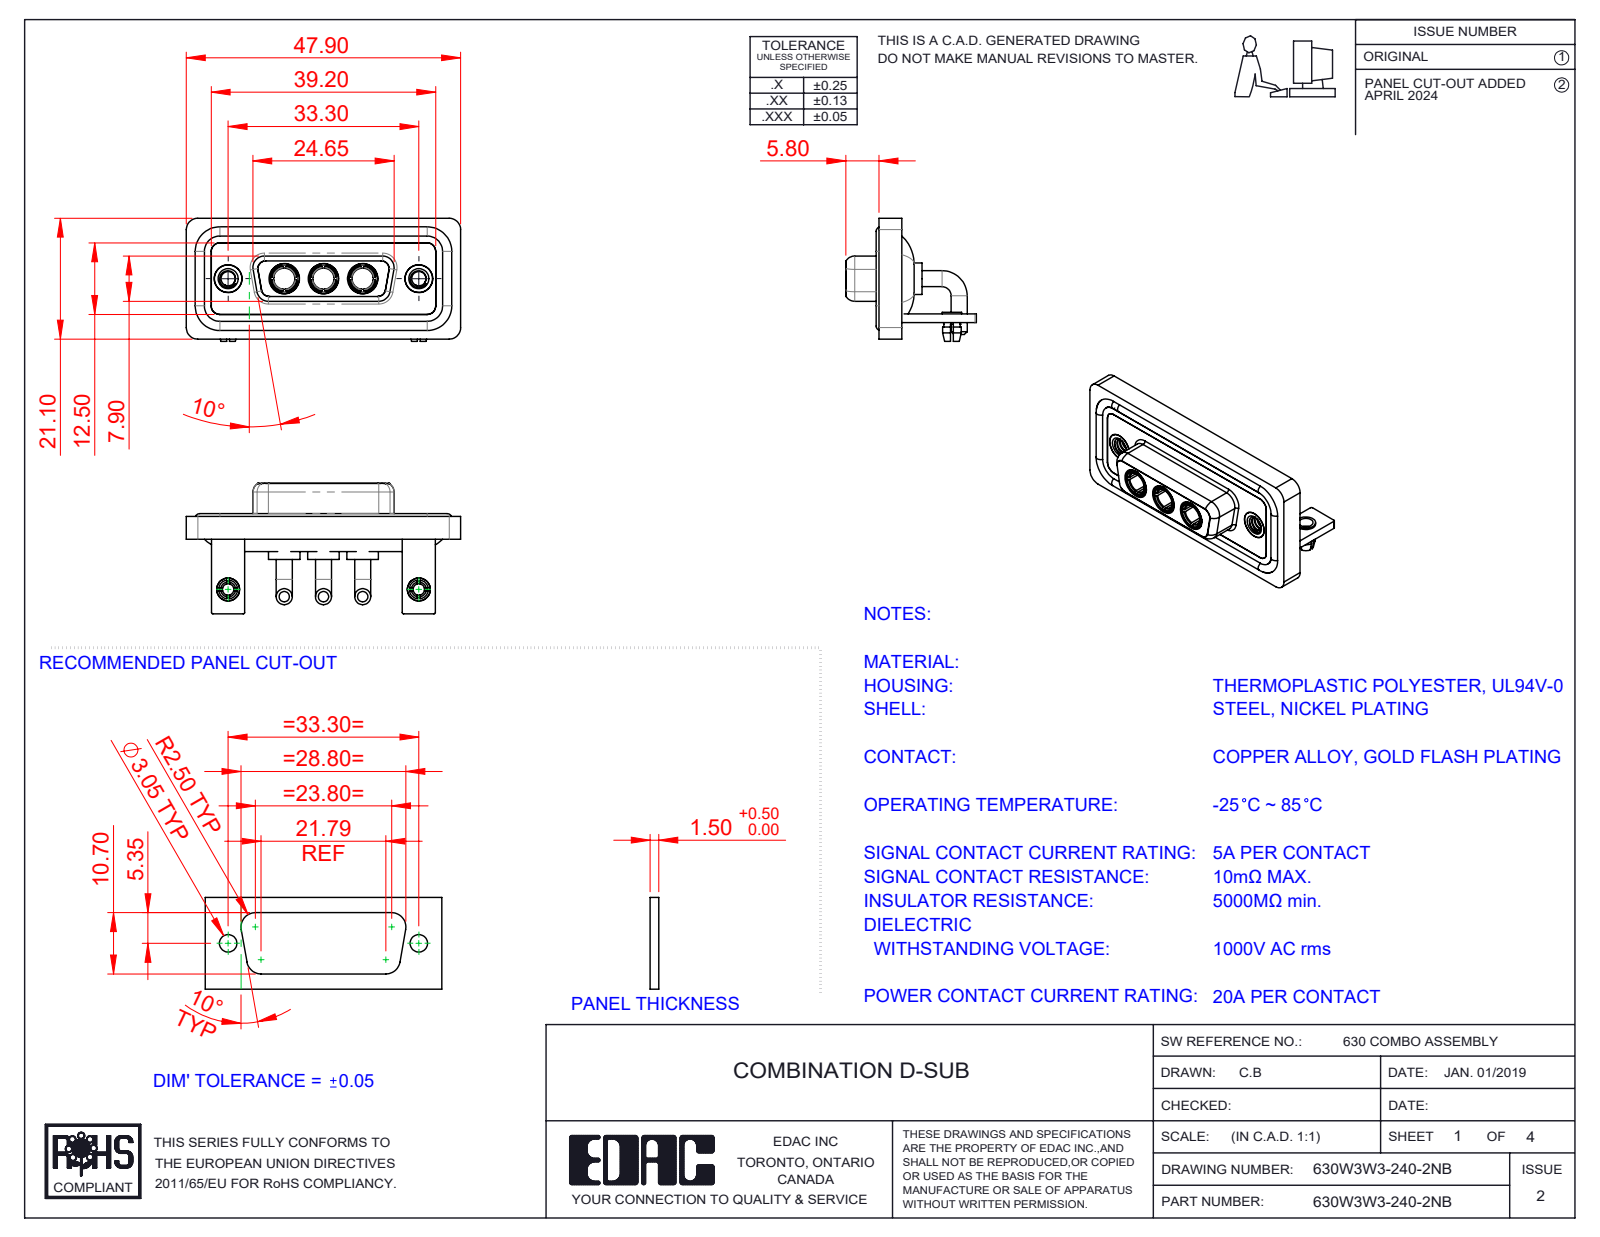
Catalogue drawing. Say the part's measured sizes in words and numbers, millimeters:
The part is named "630Combo Threaded Rivet_A; 630Combo Board Lock_50 Contacts; 630W3W3-140-2NB; Power Socket_20A RA (+5 more)". Its 3-D file was written by "SolidWorks 2023 (CONFIG_CONTROL_DESIGN)". It is 17 solids with 754 faces: 260 planar, 317 cylindrical and 177 other. Overall it measures 47.9 by 22.8 by 21.5 millimeters. Its volume is 6 575 cubic millimeters and its surface area 10 921 square millimeters. Round holes: 5 of diameter 4.85, 4 of diameter 2.5, 3 of diameter 3.7, 3 of diameter 5.3, 2 of diameter 2, 2 of diameter 3.2, 2 of diameter 4, 2 of diameter 4.05, 2 of diameter 5. Round bosses or shafts: 6 of diameter 2.8, 4 of diameter 1.6, 3 of diameter 5.5, 3 of diameter 5.2, 3 of diameter 4.96, 3 of diameter 4.75, 3 of diameter 3.75, 2 of diameter 4.95. Partial cylindrical surfaces (rounded edges, fillets, slot ends): 21 of radius 2, 18 of radius 1.5, 16 of radius 0.25, 12 of radius 1.35, 8 of radius 1.6, 5 of radius 0.5, 4 of radius 0.6, 4 of radius 0.65. The main face-to-face distances are 0.4, 2.9, 1.5, 1.8, 3.7, 1.1, 4.1, 1.6, 2.5, 1.4. The hole center spacings are 6.85, 9.8, 16.65, 23.5, 33.3, 13.7.
